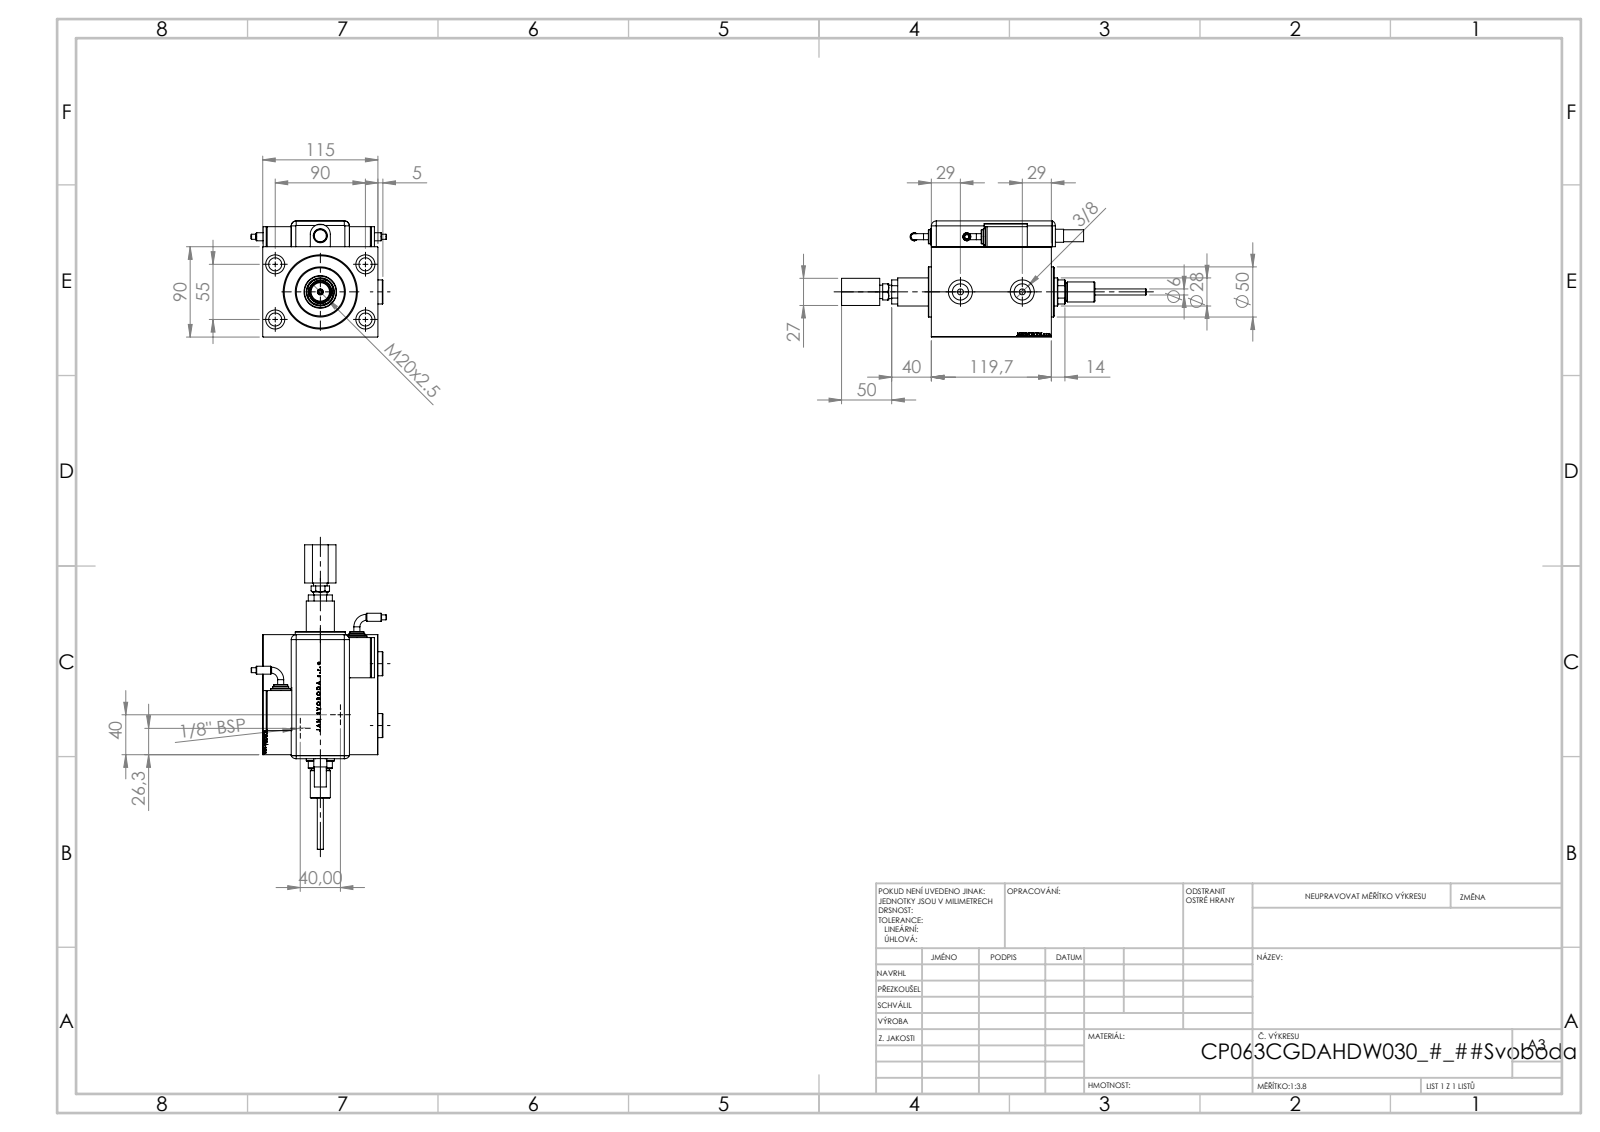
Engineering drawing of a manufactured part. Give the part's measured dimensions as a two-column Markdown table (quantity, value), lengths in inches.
| quantity | value |
| --- | --- |
| part name | SWITCH_Q_FRONT_BACK; PLUG; TYC; KRYT (+7 more) |
| STEP written by | SolidWorks 2019 (CONFIG_CONTROL_DESIGN) |
| units | inches |
| bodies | 13 solids, 1388 faces (664 planar, 173 cylindrical, 551 other) |
| overall size | 11.957 × 5.315 × 4.559 |
| volume | 77.99 in³ |
| surface area | 361.8 in² |
| round holes (diameter × count) | 0.157 × 4, 0.512 × 4, 0.748 × 4, 0.236 × 3, 0.315 × 2, 0.383 × 2, 0.591 × 2, 0.637 × 2, 0.945 × 2, 0.118 × 1, 0.551 × 1, 0.728 × 1 |
| round bosses / shafts (diameter × count) | 0.787 × 3, 0.63 × 2, 0.551 × 2, 0.315 × 2, 0.236 × 2, 0.198 × 2, 1.969 × 1, 0.709 × 1 |
| partial cylindrical surfaces (radius × count) | 0.197 × 9, 0.394 × 1, 0.531 × 1 |
| main face-to-face distances | 3.543, 0.118, 4.528, 4.713, 0.039, 0.689, 4.024, 1.181, 1.016, 4.559 |
| hole center spacings | 2.076, 2.097, 2.165, 3.543, 3.734, 4.153, 0.787, 0.873 |
